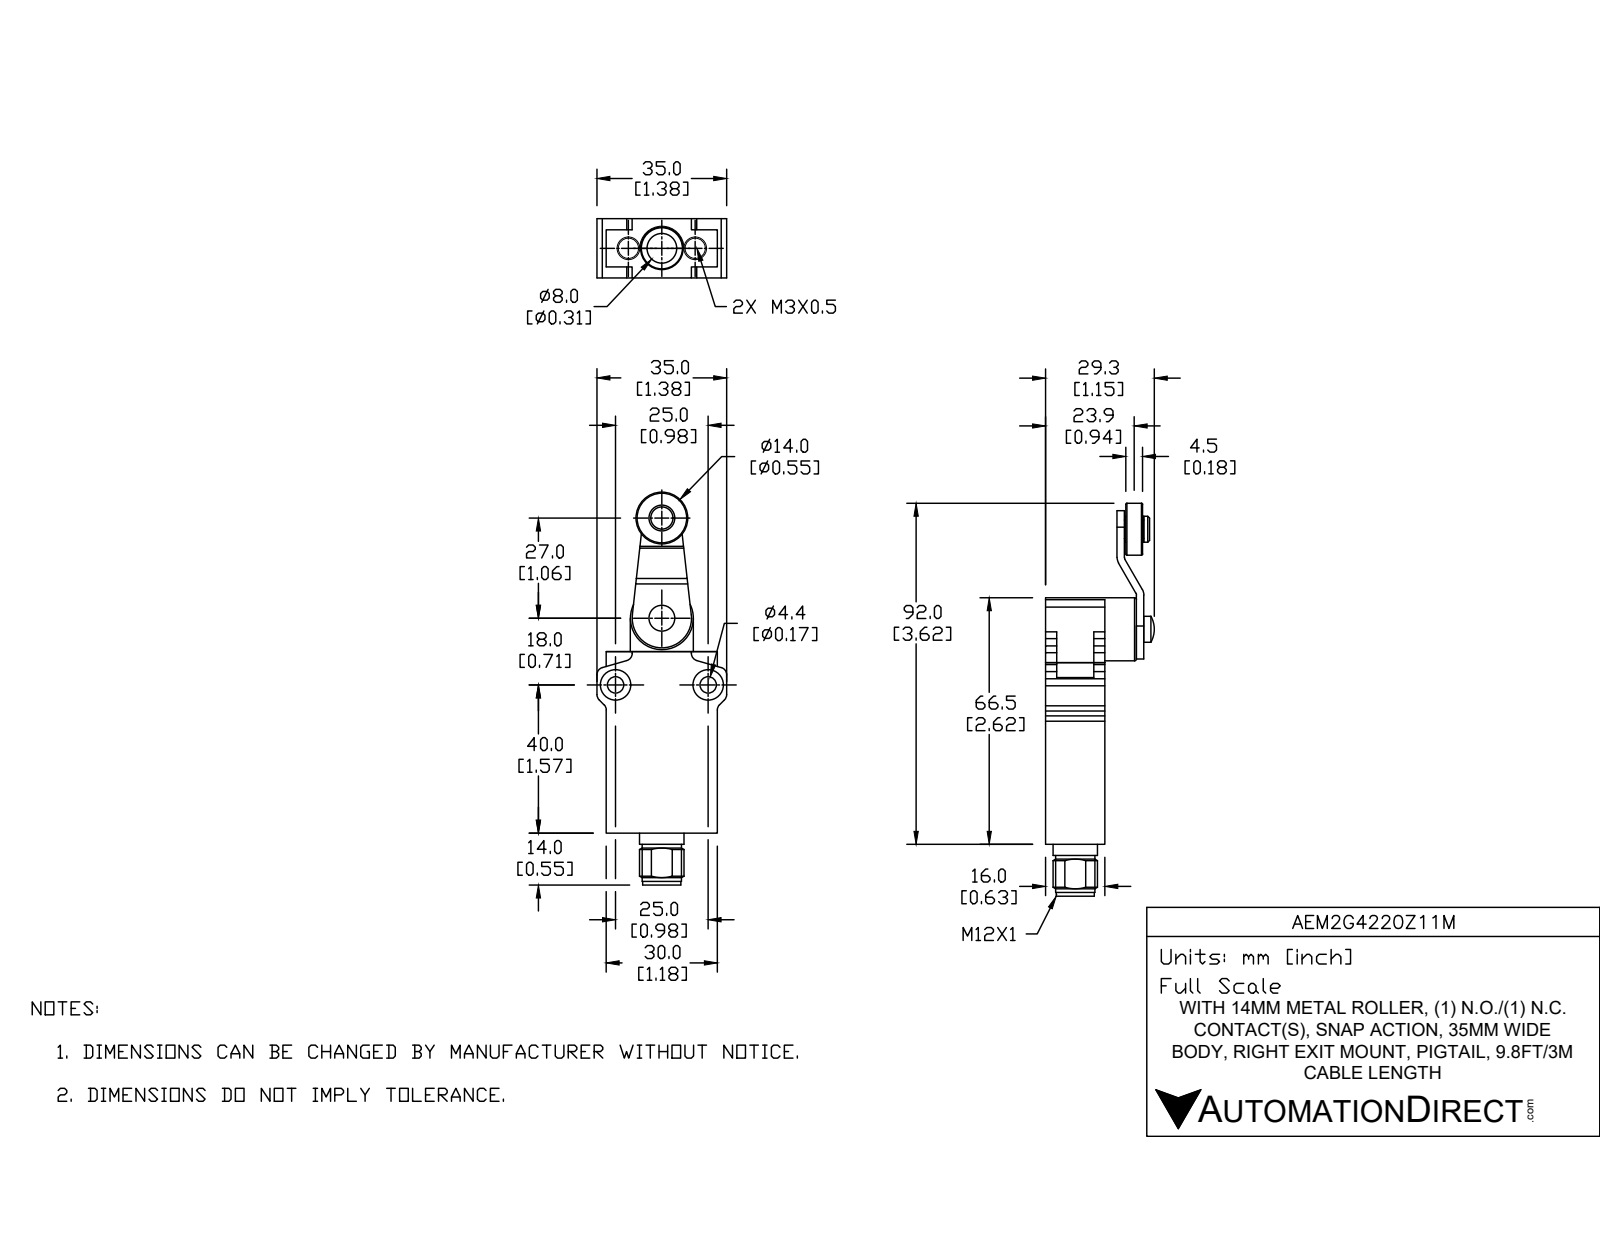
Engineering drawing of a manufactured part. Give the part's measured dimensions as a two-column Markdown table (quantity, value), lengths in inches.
| quantity | value |
| --- | --- |
| part name | AEM2G4220Z11M |
| STEP written by | SolidWorks 2017 (AUTOMOTIVE_DESIGN) |
| units | inches |
| bodies | 6 solids, 594 faces (300 planar, 93 cylindrical, 201 other) |
| overall size | 4.272 × 1.378 × 1.26 |
| volume | 1.981 in³ |
| surface area | 18.28 in² |
| round holes (diameter × count) | 0.118 × 2, 0.173 × 2, 0.323 × 2, 0.098 × 1, 0.138 × 1, 0.161 × 1, 0.197 × 1, 0.224 × 1 |
| round bosses / shafts (diameter × count) | 0.276 × 2, 0.622 × 1, 0.551 × 1, 0.472 × 1, 0.417 × 1, 0.406 × 1, 0.394 × 1, 0.236 × 1 |
| partial cylindrical surfaces (radius × count) | 0.079 × 8, 0.039 × 2, 0.118 × 2, 0.256 × 1, 0.315 × 1 |
| main face-to-face distances | 0.63, 1.181, 0.354, 0.079, 2.047, 0.984, 0.102, 0.472, 0.433, 0.898 |
| hole center spacings | 0.748, 0.861, 0.865, 0.984, 1.043, 1.819, 1.821 |
